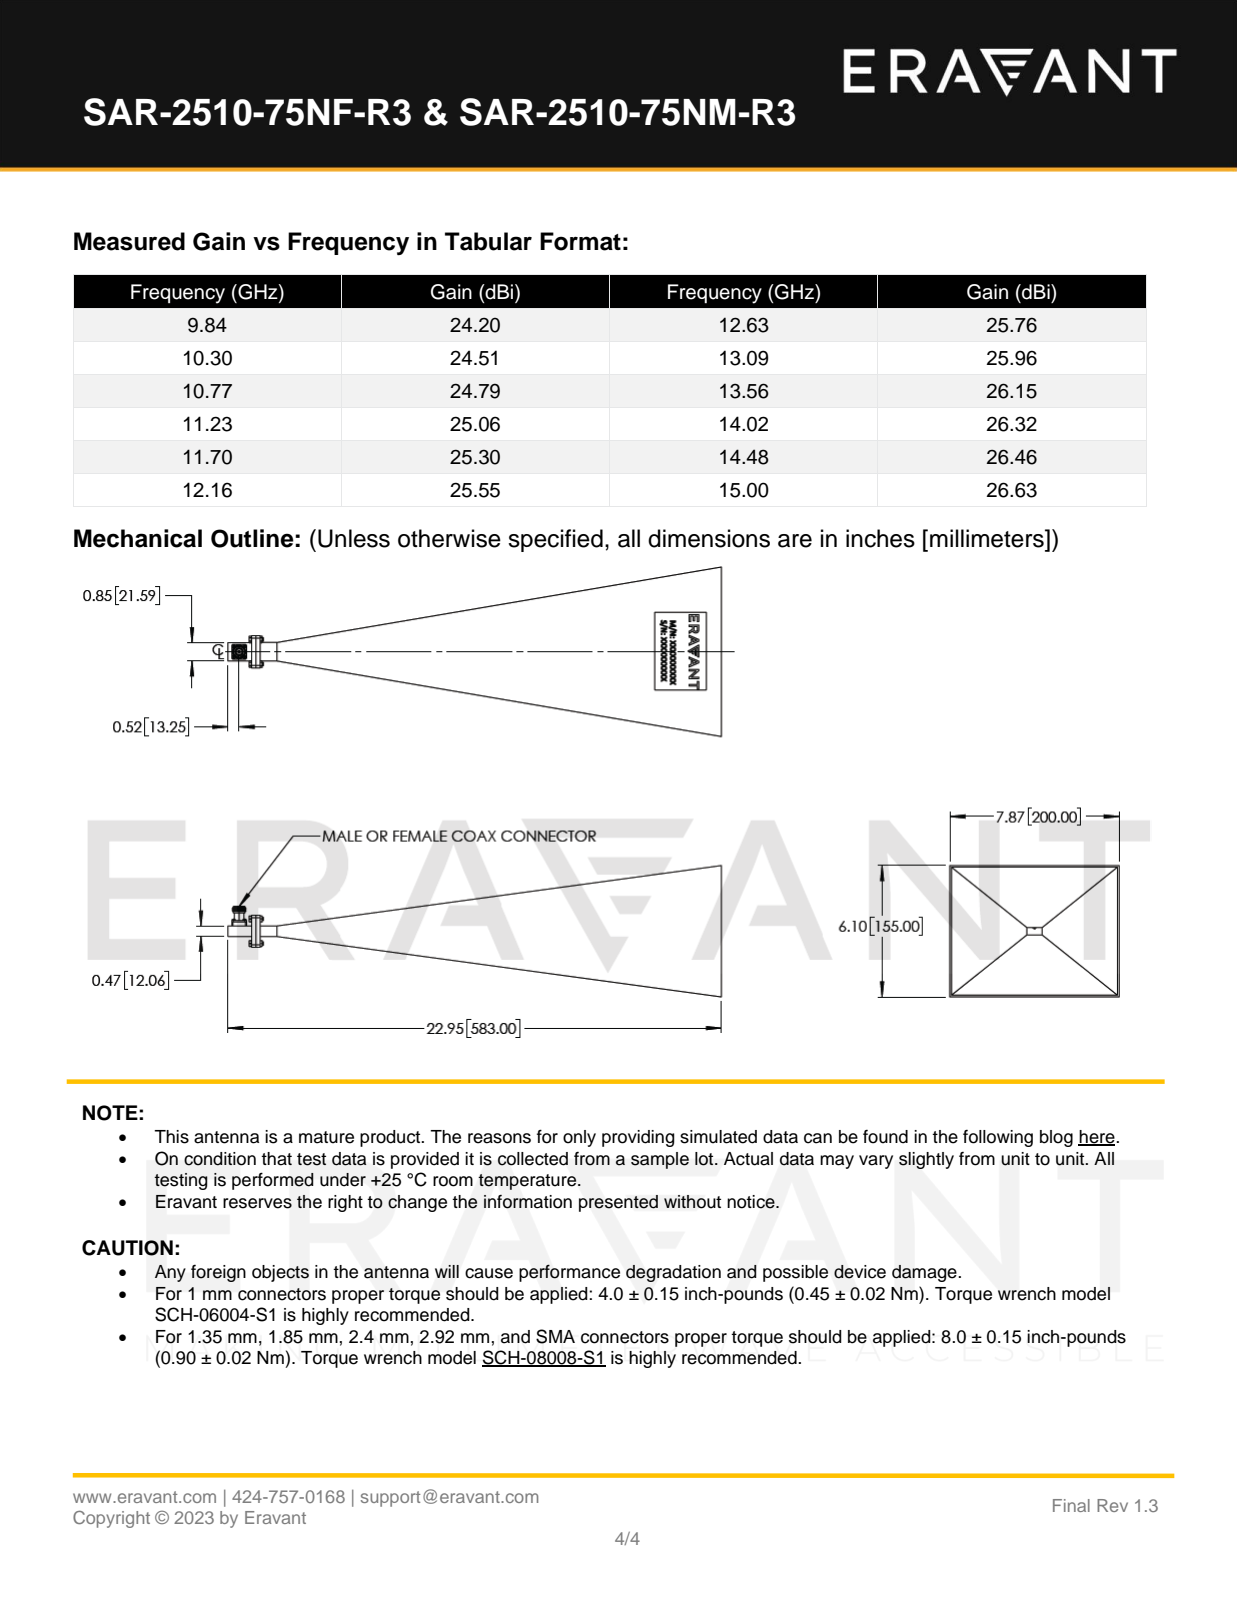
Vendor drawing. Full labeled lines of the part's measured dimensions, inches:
Part name (STEP PRODUCT): AR-7C3-R-H1
STEP written by: SolidWorks 2021 (CONFIG_CONTROL_DESIGN)
Units: inches
Bodies: 0 solids, 564 faces (215 planar, 161 cylindrical, 188 other)
Overall size (bounding box): 22.953 × 7.874 × 6.102
Round holes (diameter × count): ⌀0.118 ×4, ⌀0.131 ×4, ⌀0.164 ×4, ⌀0.067 ×1, ⌀0.276 ×1
Round bosses / shafts (diameter × count): ⌀0.157 ×8, ⌀0.138 ×4, ⌀0.098 ×4, ⌀0.079 ×4, ⌀0.625 ×1, ⌀0.531 ×1, ⌀0.433 ×1, ⌀0.12 ×1
Partial cylindrical surfaces — rounded edges, fillets, slot ends (radius × count): R0.011 ×24, R0.02 ×24, R0.079 ×4, R0.118 ×4
Main face-to-face distances: 21.457, 0.394, 21.85, 1.496, 0.485, 0.5, 0.996, 0.323, 1.173, 0.511
Hole centre spacings: 0.354, 0.5, 1.142, 0.707, 1.615
